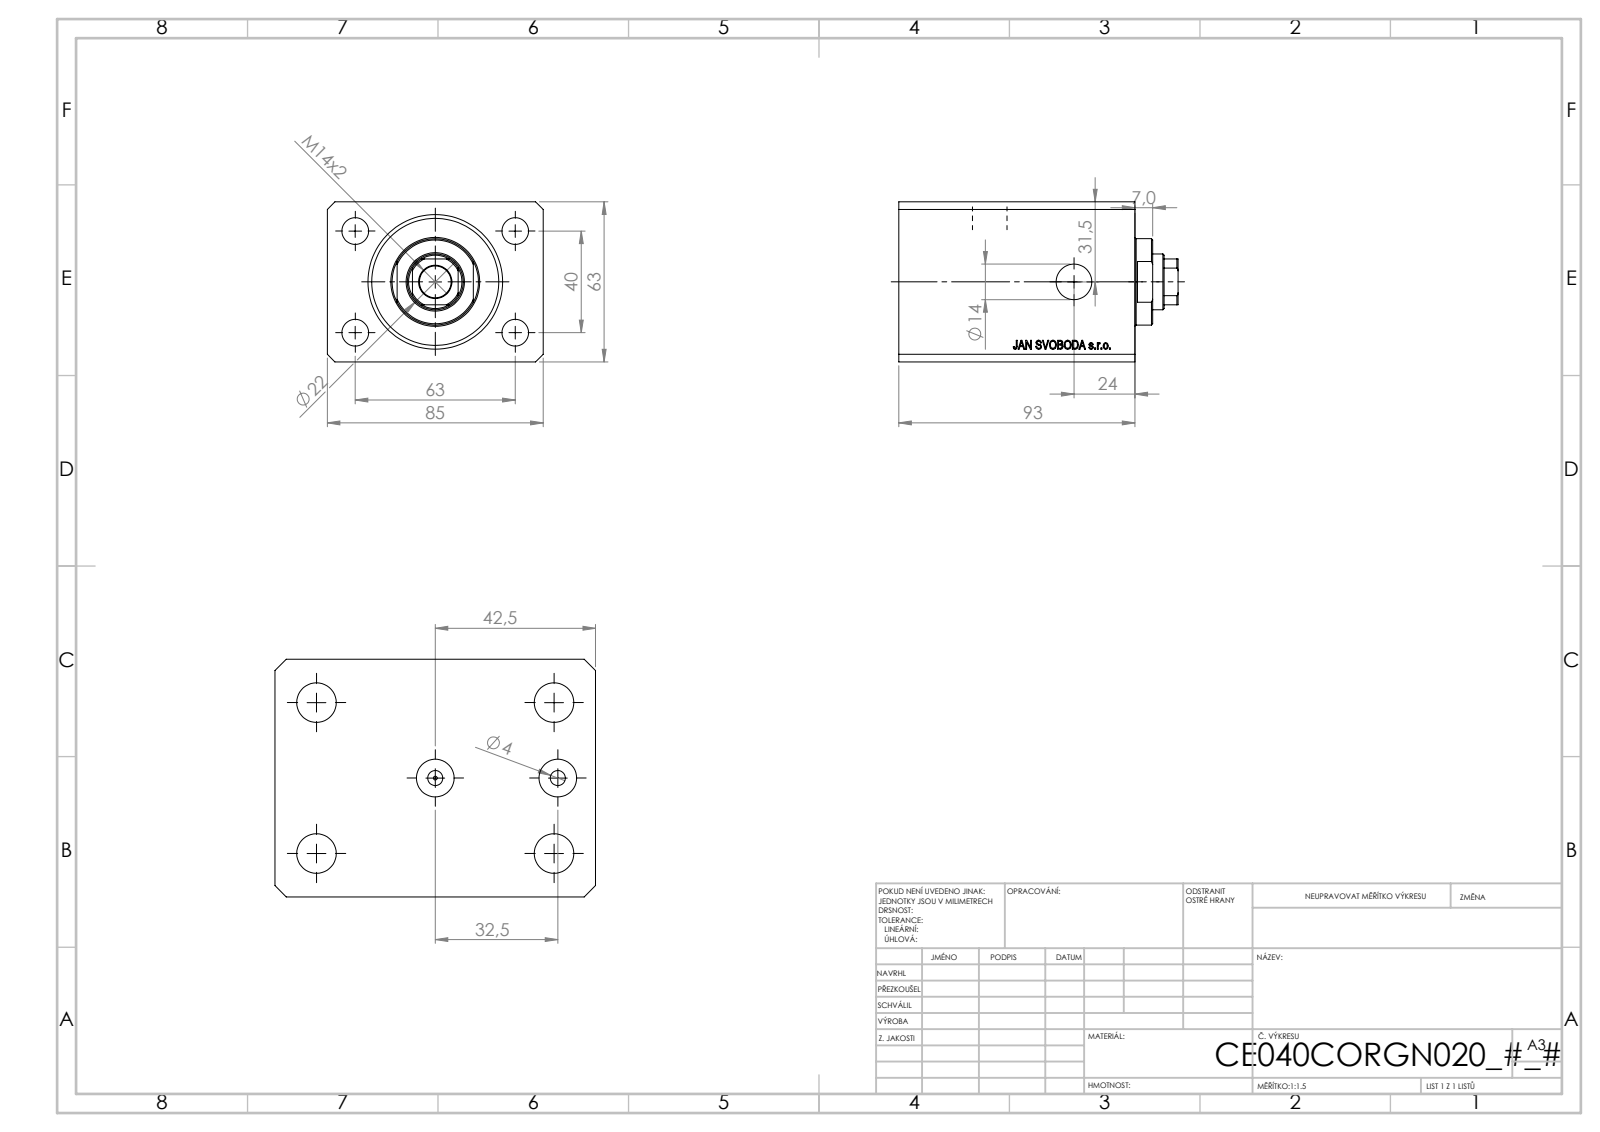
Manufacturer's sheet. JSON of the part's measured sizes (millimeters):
{"part_name": "V250CE_C_Body; V250CE_VC_C; V250CE_C_VCP", "step_written_by": "SolidWorks 2019 (CONFIG_CONTROL_DESIGN)", "units": "millimeters", "bodies": {"solids": 3, "faces": 866, "planar": 428, "cylindrical": 44, "other": 394}, "overall_size": [110, 85, 63], "volume_mm3": 449801, "surface_area_mm2": 83942, "round_holes": [[10.5, 4], [4, 3], [10, 2], [14, 2], [1.25, 1], [12.5, 1], [22, 1], [40, 1], [53, 1]], "round_bosses_or_shafts": [[34, 1]], "partial_cylinders_radius": [[10.5, 1]], "face_to_face_distances": [63, 85, 93, 17, 76, 11.4, 64.6, 81.6, 56, 44.6], "hole_center_spacings": [37.31, 20.02, 40, 63, 67.05, 74.63, 32.5, 45]}
